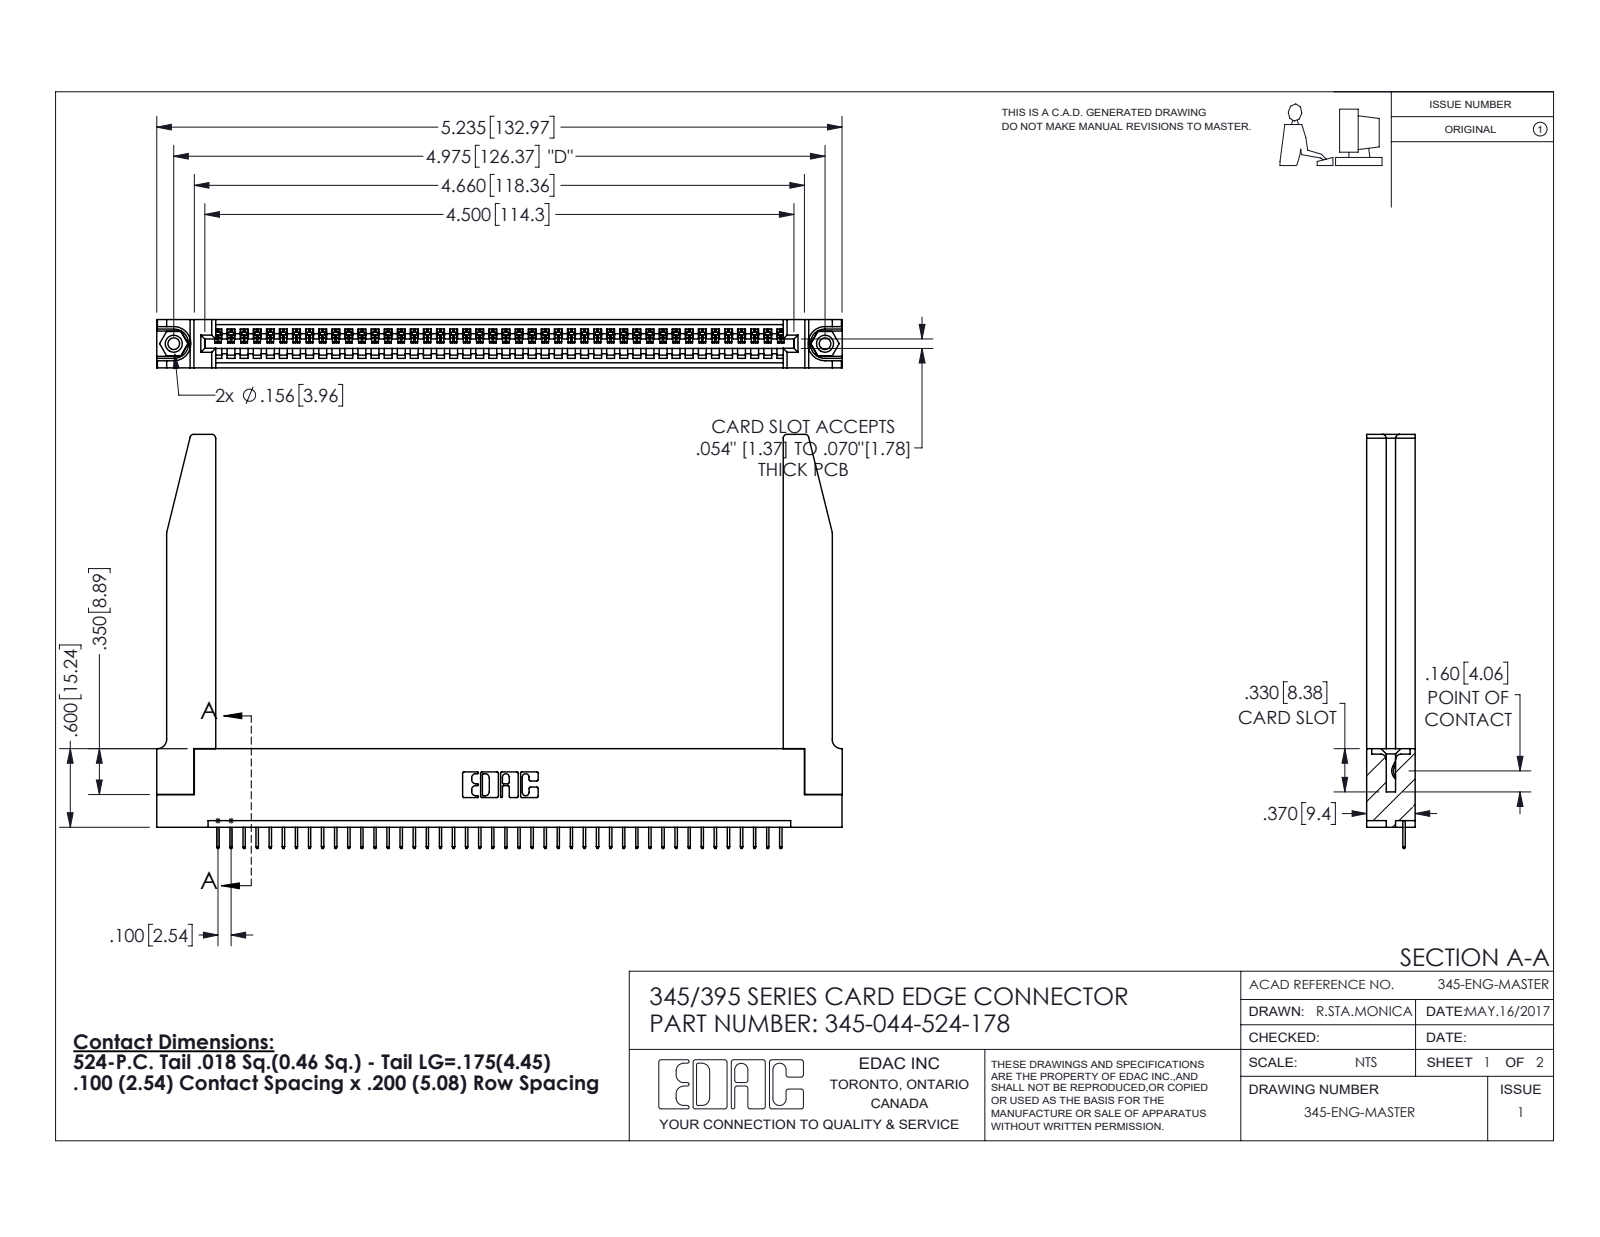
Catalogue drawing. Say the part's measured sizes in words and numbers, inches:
The part is named "345-220-078_345-220-078; 345-250-001_345-250-001-102; 345-044-524-178; 345 Part_Flush Mounting Lugs - 0.156 Dia-TH (+1 more)". Its 3-D file was written by "SolidWorks 2016 (CONFIG_CONTROL_DESIGN)". It is 49 solids with 3088 faces: 2246 planar, 790 cylindrical and 52 other. Overall it measures 5.236 by 3.162 by 0.37 inches. Its volume is 1.235 cubic inches and its surface area 35.49 square inches. Round holes: 2 of diameter 0.089, 2 of diameter 0.125, 2 of diameter 0.156, 1 of diameter 0.064. Round bosses or shafts: 2 of diameter 0.155. Partial cylindrical surfaces (rounded edges, fillets, slot ends): 88 of radius 0.006, 22 of radius 0.01, 8 of radius 0.03, 6 of radius 0.007, 6 of radius 0.031, 3 of radius 0.026, 2 of radius 0.031, 2 of radius 0.04. The main face-to-face distances are 0.37, 0.072, 0.298, 0.2, 0.098, 0.272, 0.025, 0.225, 0.148, 0.15. The hole center spacings are 0.27, 4.739, 4.975.
